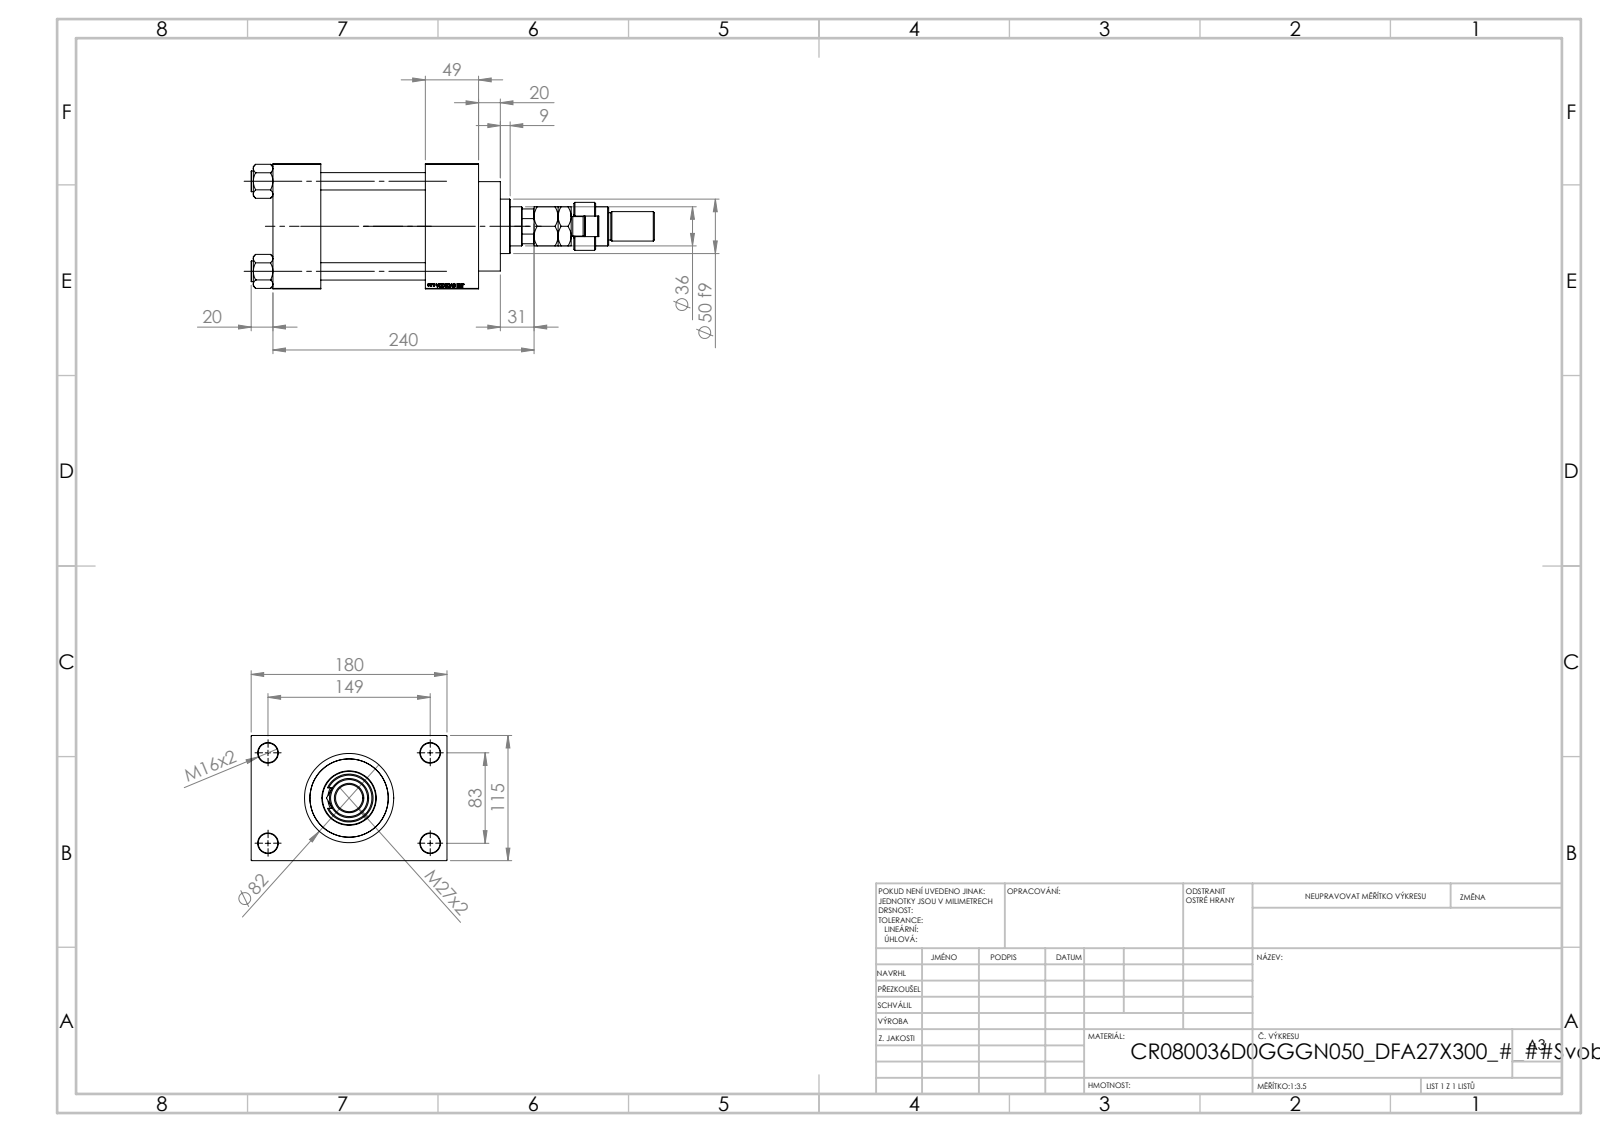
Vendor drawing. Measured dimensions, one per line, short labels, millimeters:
name: NUT_M5_D; FEMALE_PART_FOR_DFA; MFA; V215CR_D_Body (+3 more)
written by: SolidWorks 2019 (CONFIG_CONTROL_DESIGN)
unit: mm
bodies: 13 solids, 1237 faces (573 planar, 102 cylindrical, 562 other)
size: 370.5 × 180 × 115
volume: 2 174 000 mm³; area: 340 092 mm²
holes: 4× ⌀16, 4× ⌀18, 2× ⌀7, 2× ⌀26.44, 2× ⌀35, 1× ⌀25.5, 1× ⌀39, 1× ⌀61, 1× ⌀72, 1× ⌀80
bosses: 4× ⌀19, 1× ⌀86, 1× ⌀82, 1× ⌀50, 1× ⌀44, 1× ⌀36, 1× ⌀28, 1× ⌀27
rounds: 1× R9.5, 1× R15, 1× R17.5
face distances: 115, 96, 145, 49, 44, 140, 189, 32.5, 147.5, 180
hole spacings: 33.15, 58.48, 82.7, 85.28, 89.24, 115.85, 142.43, 83
